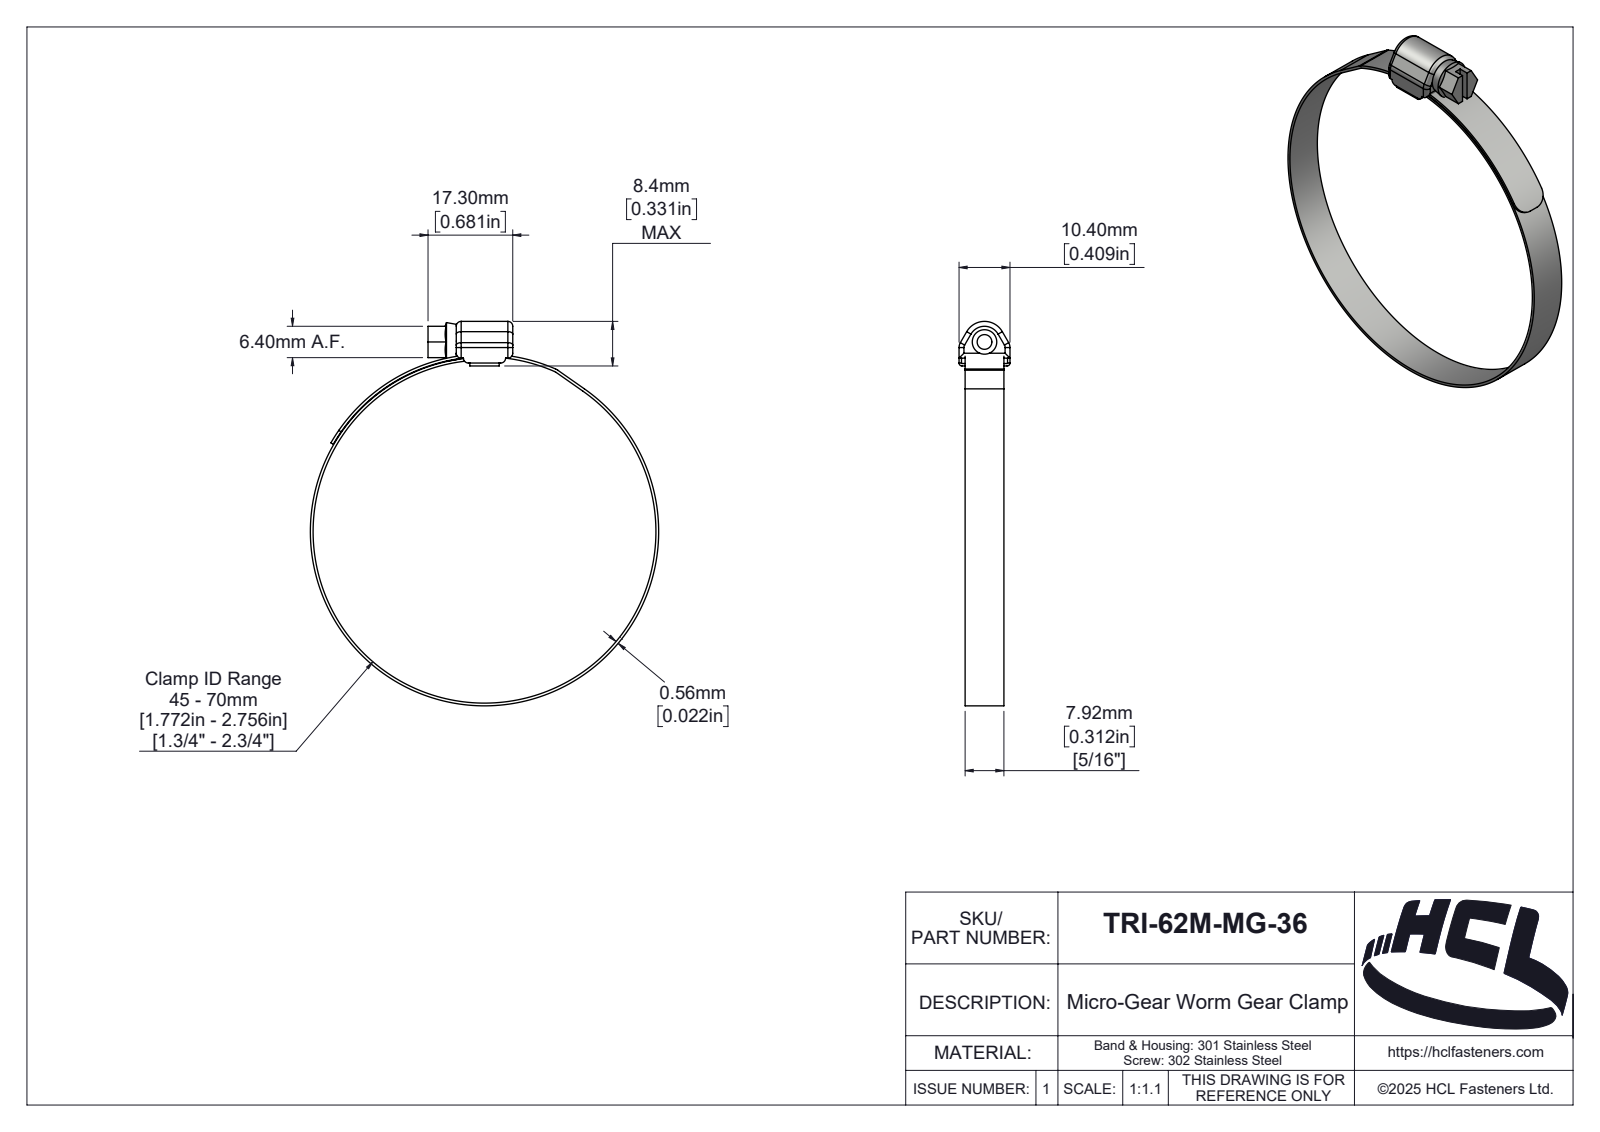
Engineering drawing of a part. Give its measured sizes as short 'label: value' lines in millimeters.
name: TRI-62M-MG-36
written by: SolidWorks 2025 (AUTOMOTIVE_DESIGN)
unit: mm
bodies: 3 solids, 186 faces (38 planar, 87 cylindrical, 61 other)
size: 78.46 × 71.12 × 10.4
volume: 2 093 mm³; area: 5 570 mm²
holes: 1× ⌀5, 1× ⌀70
bosses: 1× ⌀71.12
rounds: 12× R1, 3× R2, 2× R0.1, 2× R0.6, 2× R3, 1× R0.25, 1× R1.01, 1× R1.26
face distances: 7.92, 1.1, 0.5, 1.24, 9.16, 1.6, 0.56, 6.2, 10.4, 5.76
